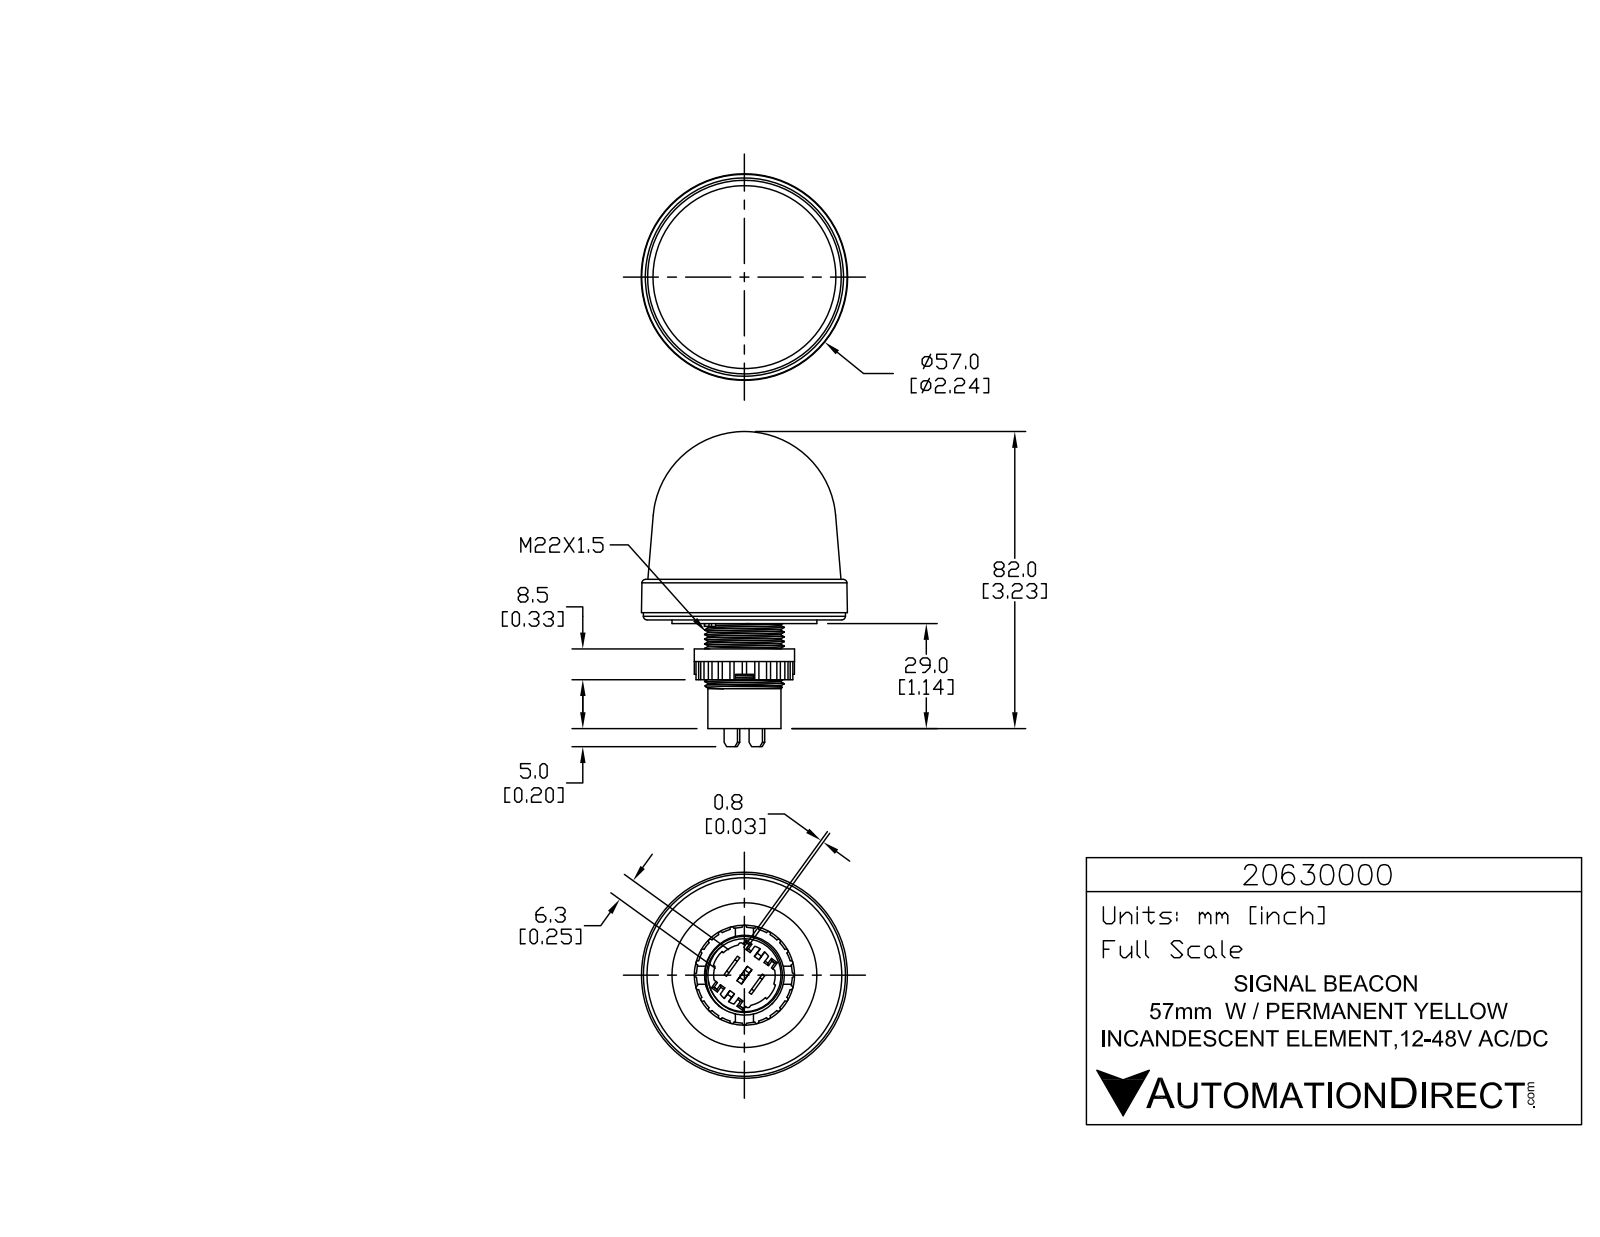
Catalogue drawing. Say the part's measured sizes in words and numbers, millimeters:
The part is named "20630000". Its 3-D file was written by "SolidWorks 2015 (AUTOMOTIVE_DESIGN)". It is 1 solid with 1002 faces: 637 planar, 266 cylindrical and 99 other. Overall it measures 86.7 by 56.9 by 56.9 millimeters. Its volume is 106 200 cubic millimeters and its surface area 16 820 square millimeters. Round holes: 3 of diameter 1, 1 of diameter 23. Round bosses or shafts: 3 of diameter 5.7, 3 of diameter 1.4, 1 of diameter 55.8, 1 of diameter 40, 1 of diameter 27.7, 1 of diameter 22, 1 of diameter 20.2. Partial cylindrical surfaces (rounded edges, fillets, slot ends): 24 of radius 0.6, 6 of radius 0.2, 6 of radius 0.2, 6 of radius 0.2, 6 of radius 3.3, 3 of radius 0.1, 3 of radius 0.1, 3 of radius 0.2. The main face-to-face distances are 1, 7, 8.5, 8, 27, 19, 26, 3, 29, 10.5.
